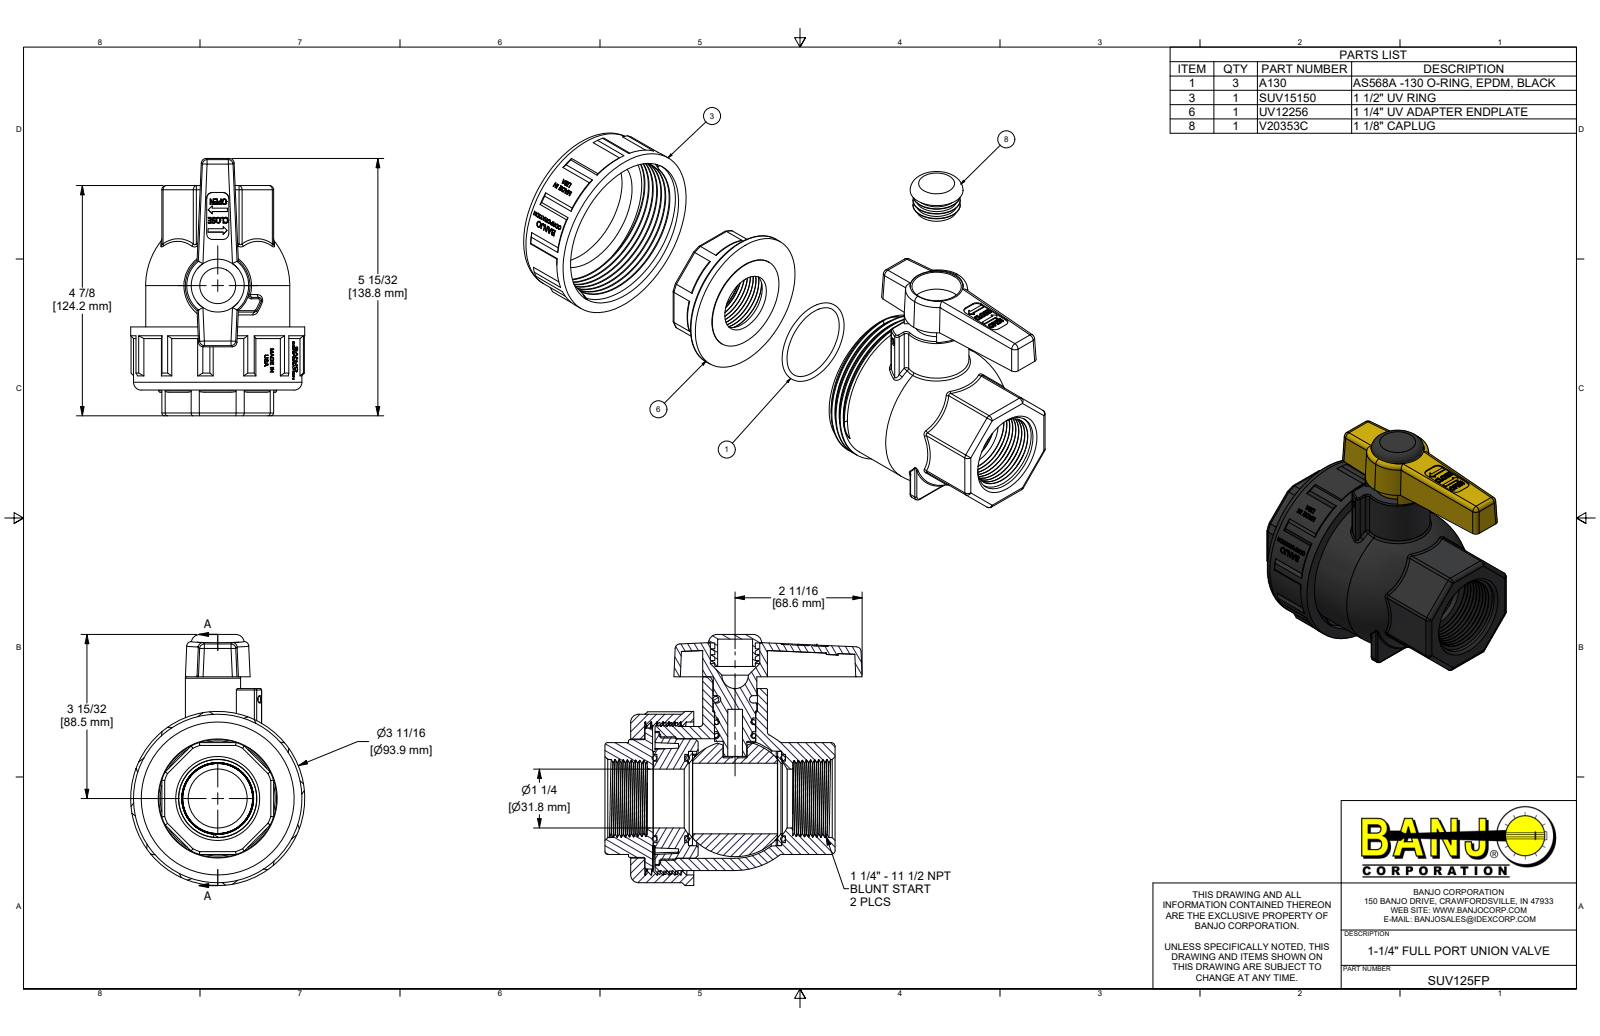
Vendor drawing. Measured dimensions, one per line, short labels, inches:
name: SUV125FP; UV12254; SUV15153; SUV15150 (+8 more)
written by: Autodesk Inventor 2022 (AUTOMOTIVE_DESIGN)
unit: in
bodies: 15 solids, 1170 faces (514 planar, 220 cylindrical, 436 other)
size: 5.465 × 5.331 × 3.697
volume: 26.59 in³; area: 257.1 in²
holes: 1× ⌀0.313, 1× ⌀0.563, 1× ⌀0.744, 1× ⌀0.878, 1× ⌀0.948, 1× ⌀1.05, 1× ⌀1.125, 1× ⌀1.25, 1× ⌀1.5, 1× ⌀1.875, 1× ⌀2.005, 1× ⌀2.006
bosses: 1× ⌀3.697, 1× ⌀3.577, 1× ⌀3.226, 1× ⌀3.06, 1× ⌀2.995, 1× ⌀2.8, 1× ⌀2.62, 1× ⌀2.535
rounds: 16× R0.09, 11× R0.06, 10× R0.1, 8× R0.03, 6× R0.125, 4× R0.848, 1× R0.479, 1× R0.987
face distances: 0.165, 2.375, 0.04, 0.052, 0.465, 0.3, 0.217, 0.517, 0.875, 0.012
